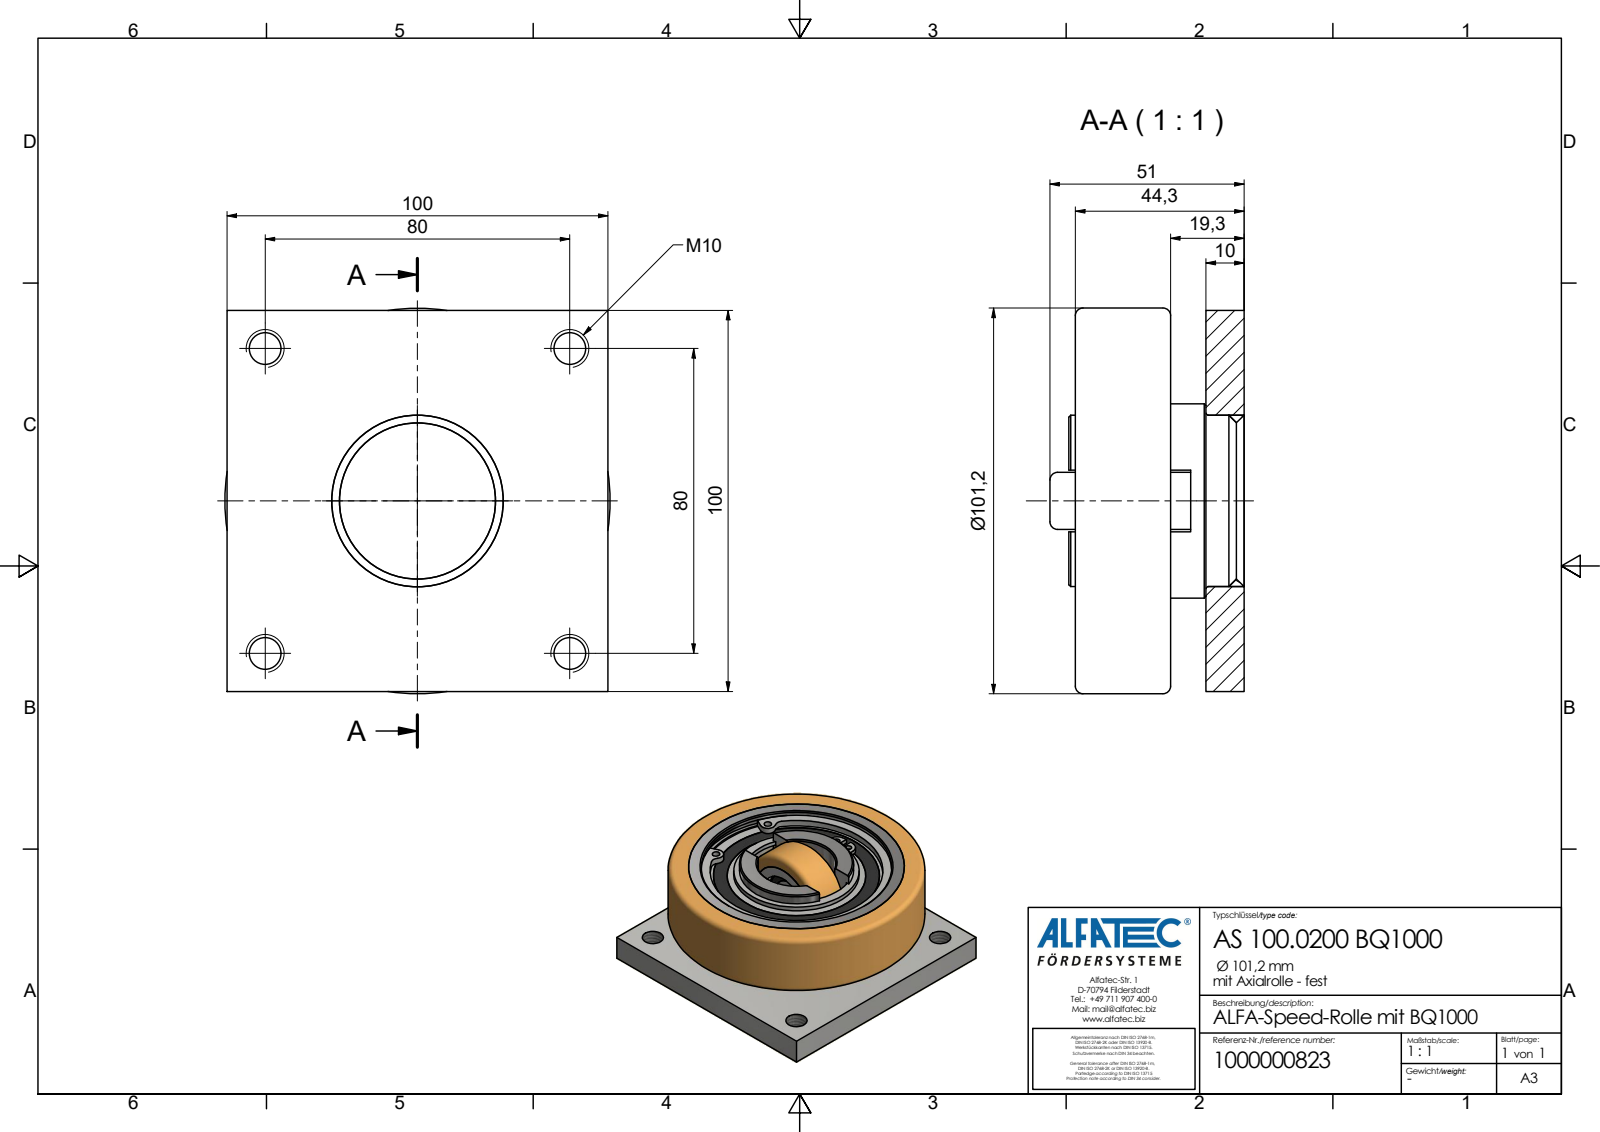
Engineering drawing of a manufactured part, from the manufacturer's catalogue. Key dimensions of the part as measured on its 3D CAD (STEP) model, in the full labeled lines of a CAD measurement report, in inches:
Part name (STEP PRODUCT): AS 100.0200 BQ1000_Kontur
STEP written by: Autodesk Inventor 2020 (AP242_MANAGED_MODEL_BASED_3D_ENGINEERING_MIM_LF)
Units: inches
Bodies: 2 solids, 108 faces (54 planar, 30 cylindrical, 24 other)
Overall size (bounding box): 3.984 × 3.984 × 2.008
Volume: 37.27 in³ · Surface area: 151.9 in²
Round holes (diameter × count): ⌀0.33 ×4, ⌀1.22 ×1
Round bosses / shafts (diameter × count): ⌀3.984 ×1, ⌀2.008 ×1
Partial cylindrical surfaces — rounded edges, fillets, slot ends (radius × count): R0.512 ×1, R0.535 ×1, R0.787 ×1, R0.886 ×1
Main face-to-face distances: 0.394, 1.744, 1.35, 0.76, 0.366, 0.984, 3.937, 0.079, 0.315, 0.681
Hole centre spacings: 2.227, 3.15, 4.454
